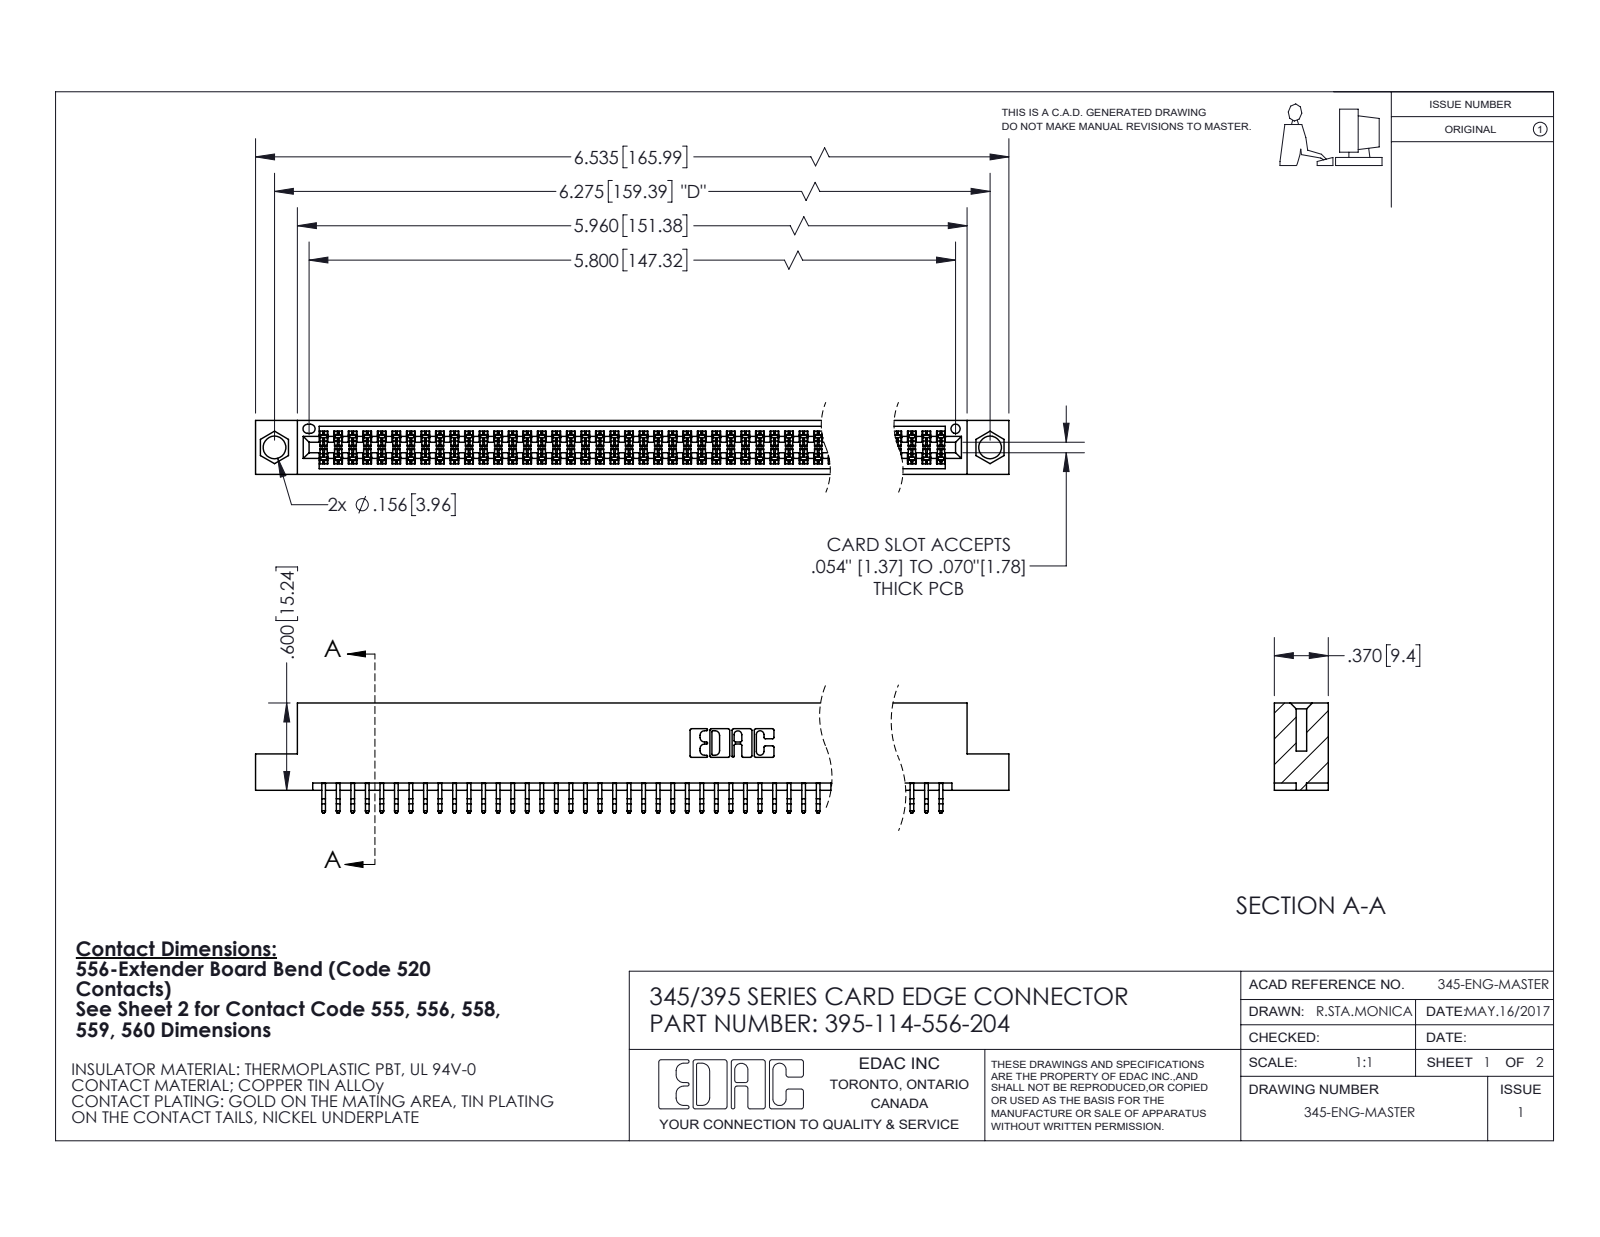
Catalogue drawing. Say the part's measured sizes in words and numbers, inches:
The part is named "395-114-556-204; 345-292-001_556 Tail; 345 Part_Flush Mounting Lugs - 0.156 Dia-TI". Its 3-D file was written by "SolidWorks 2020 (CONFIG_CONTROL_DESIGN)". It is 115 solids with 6524 faces: 4312 planar, 2212 cylindrical and 0 other. Overall it measures 6.535 by 0.757 by 0.37 inches. Its volume is 0.986 cubic inches and its surface area 37.08 square inches. Round holes: 2 of diameter 0.156, 1 of diameter 0.064. Partial cylindrical surfaces (rounded edges, fillets, slot ends): 228 of radius 0.006, 22 of radius 0.01, 6 of radius 0.007, 6 of radius 0.031, 3 of radius 0.026, 2 of radius 0.01, 2 of radius 0.014, 2 of radius 0.019. The main face-to-face distances are 0.298, 0.072, 0.37, 0.2, 0.025, 0.098, 0.272, 0.225, 0.175, 0.149. The hole center spacings are 0.27, 6.039, 6.275.
